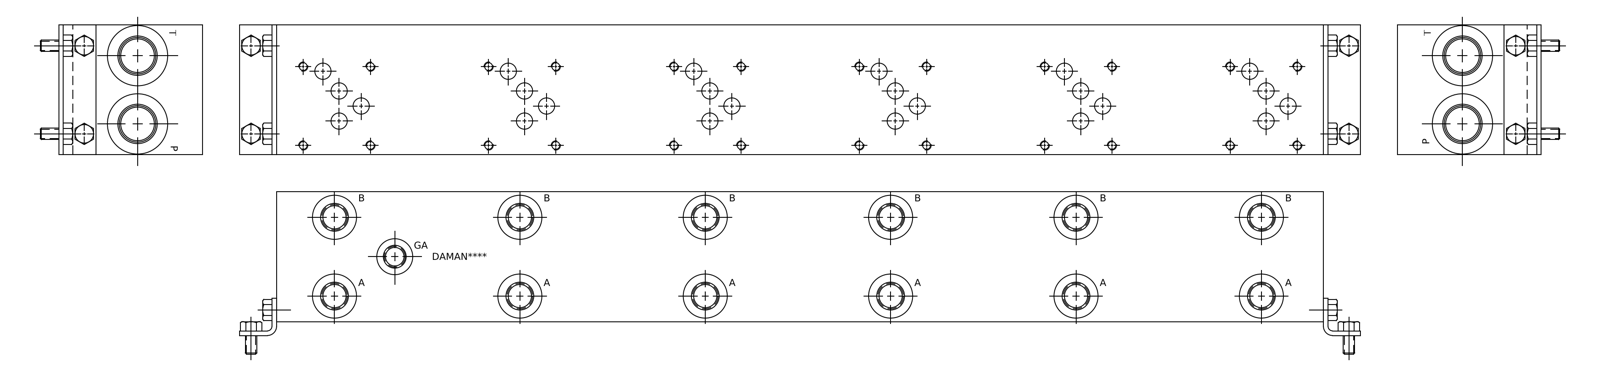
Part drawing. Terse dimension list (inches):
name: Part_AD05P065S_3D
written by: Autodesk Inventor 2020 (AUTOMOTIVE_DESIGN)
unit: in
bodies: 1 solid, 992 faces (484 planar, 165 cylindrical, 343 other)
size: 28.25 × 3.5 × 3.5
volume: 334.7 in³; area: 485.9 in²
holes: 24× ⌀0.201, 24× ⌀0.25, 24× ⌀0.438, 12× ⌀0.625, 12× ⌀0.689, 12× ⌀0.75, 12× ⌀0.758, 12× ⌀1.206, 2× ⌀0.257, 2× ⌀0.312, 2× ⌀0.906, 2× ⌀0.981
face distances: 3.5, 0.031, 3.469, 28.25, 28.219, 28.188, 0.75, 0.593, 0.562, 2.907
hole spacings: 5, 10, 15, 5.433, 15.15, 10.223, 1.813, 2.125
